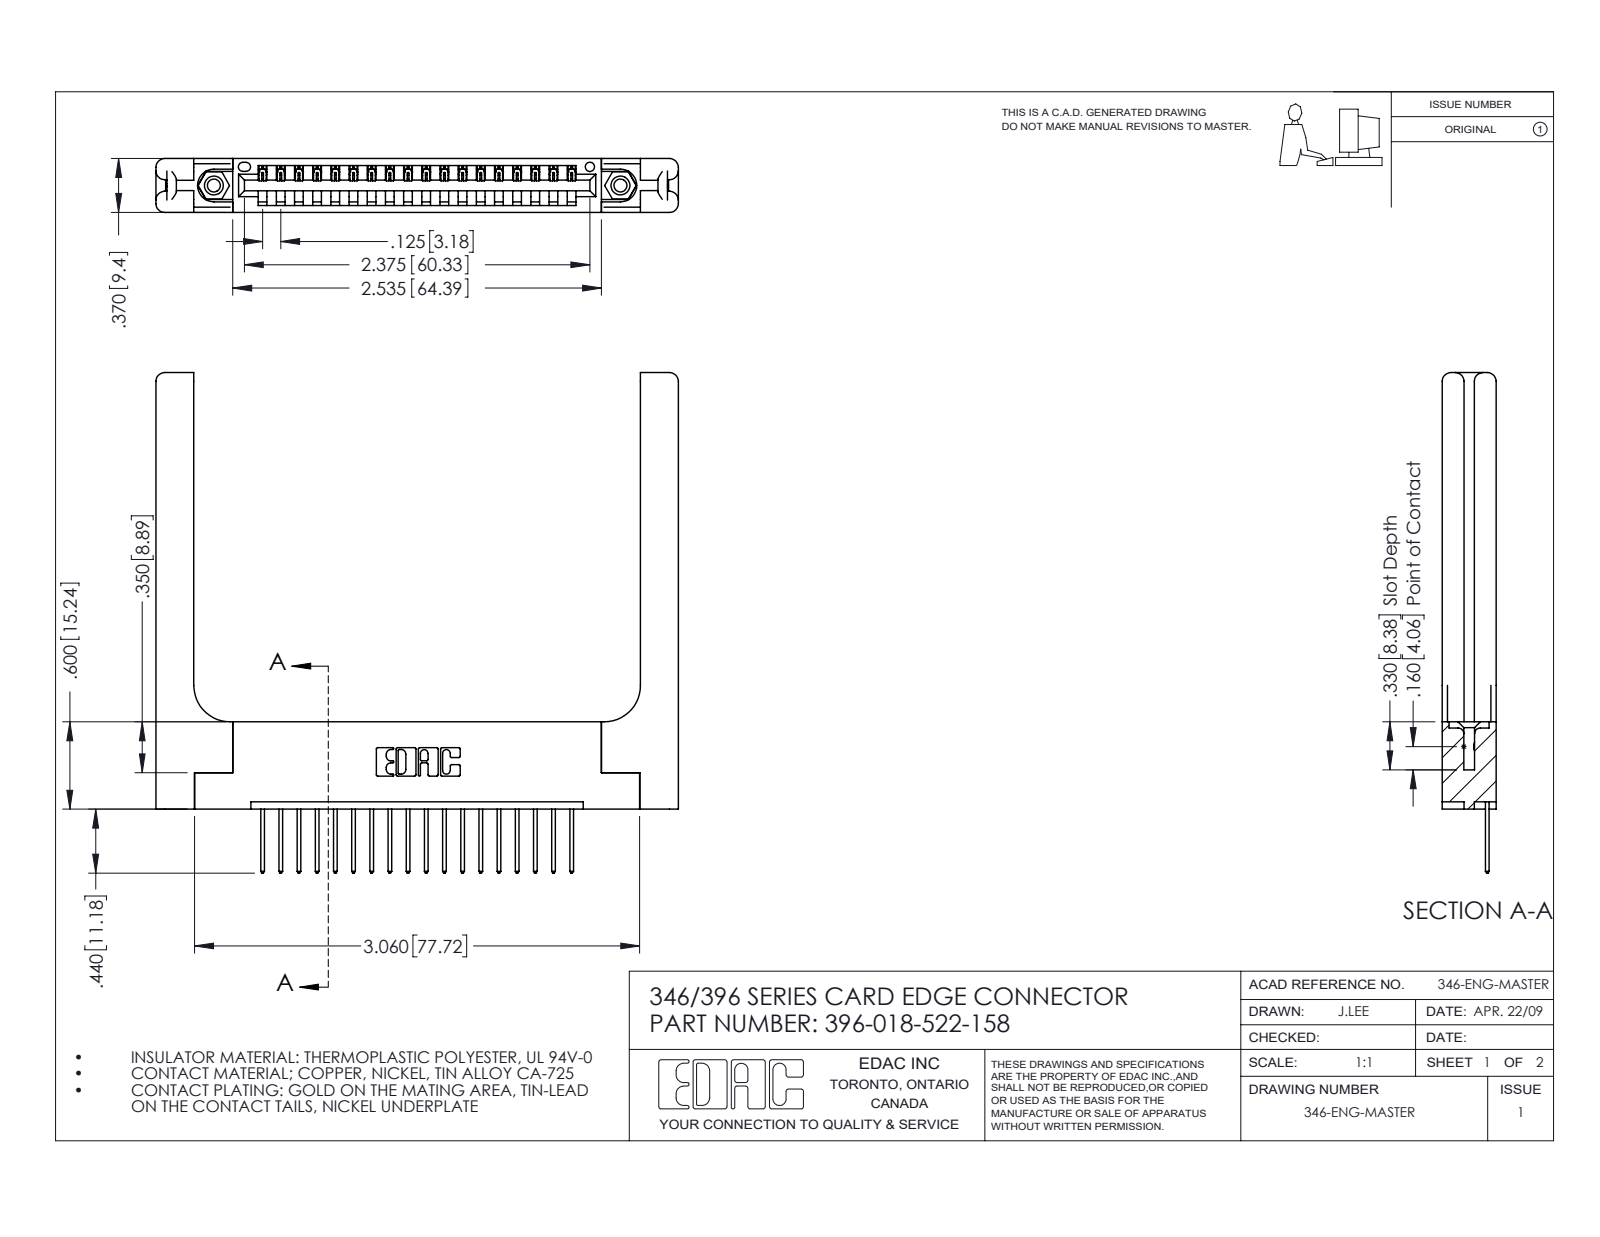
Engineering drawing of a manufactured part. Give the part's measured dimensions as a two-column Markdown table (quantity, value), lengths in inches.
| quantity | value |
| --- | --- |
| part name | 346 Part_Flush Mounting Lugs - 0.156 Dia-TH; 346-220-058_345-220-058; 345-250-001_345-250-001-102; 396-018-522-158 (+1 more) |
| STEP written by | SolidWorks 2016 (CONFIG_CONTROL_DESIGN) |
| units | inches |
| bodies | 23 solids, 1422 faces (944 planar, 418 cylindrical, 60 other) |
| overall size | 3.591 × 3.44 × 0.37 |
| volume | 0.982 in³ |
| surface area | 24.31 in² |
| round holes (diameter × count) | 0.089 × 2, 0.125 × 2, 0.156 × 2, 0.064 × 1 |
| round bosses / shafts (diameter × count) | 0.155 × 2 |
| partial cylindrical surfaces (radius × count) | 0.006 × 36, 0.01 × 36, 0.01 × 22, 0.06 × 16, 0.007 × 6, 0.031 × 6, 0.026 × 3, 0.03 × 2 |
| main face-to-face distances | 0.37, 0.072, 0.15, 0.148, 0.048, 0.322, 0.25, 0.102, 0.22, 0.173 |
| hole center spacings | 0.246, 2.588, 2.795 |
